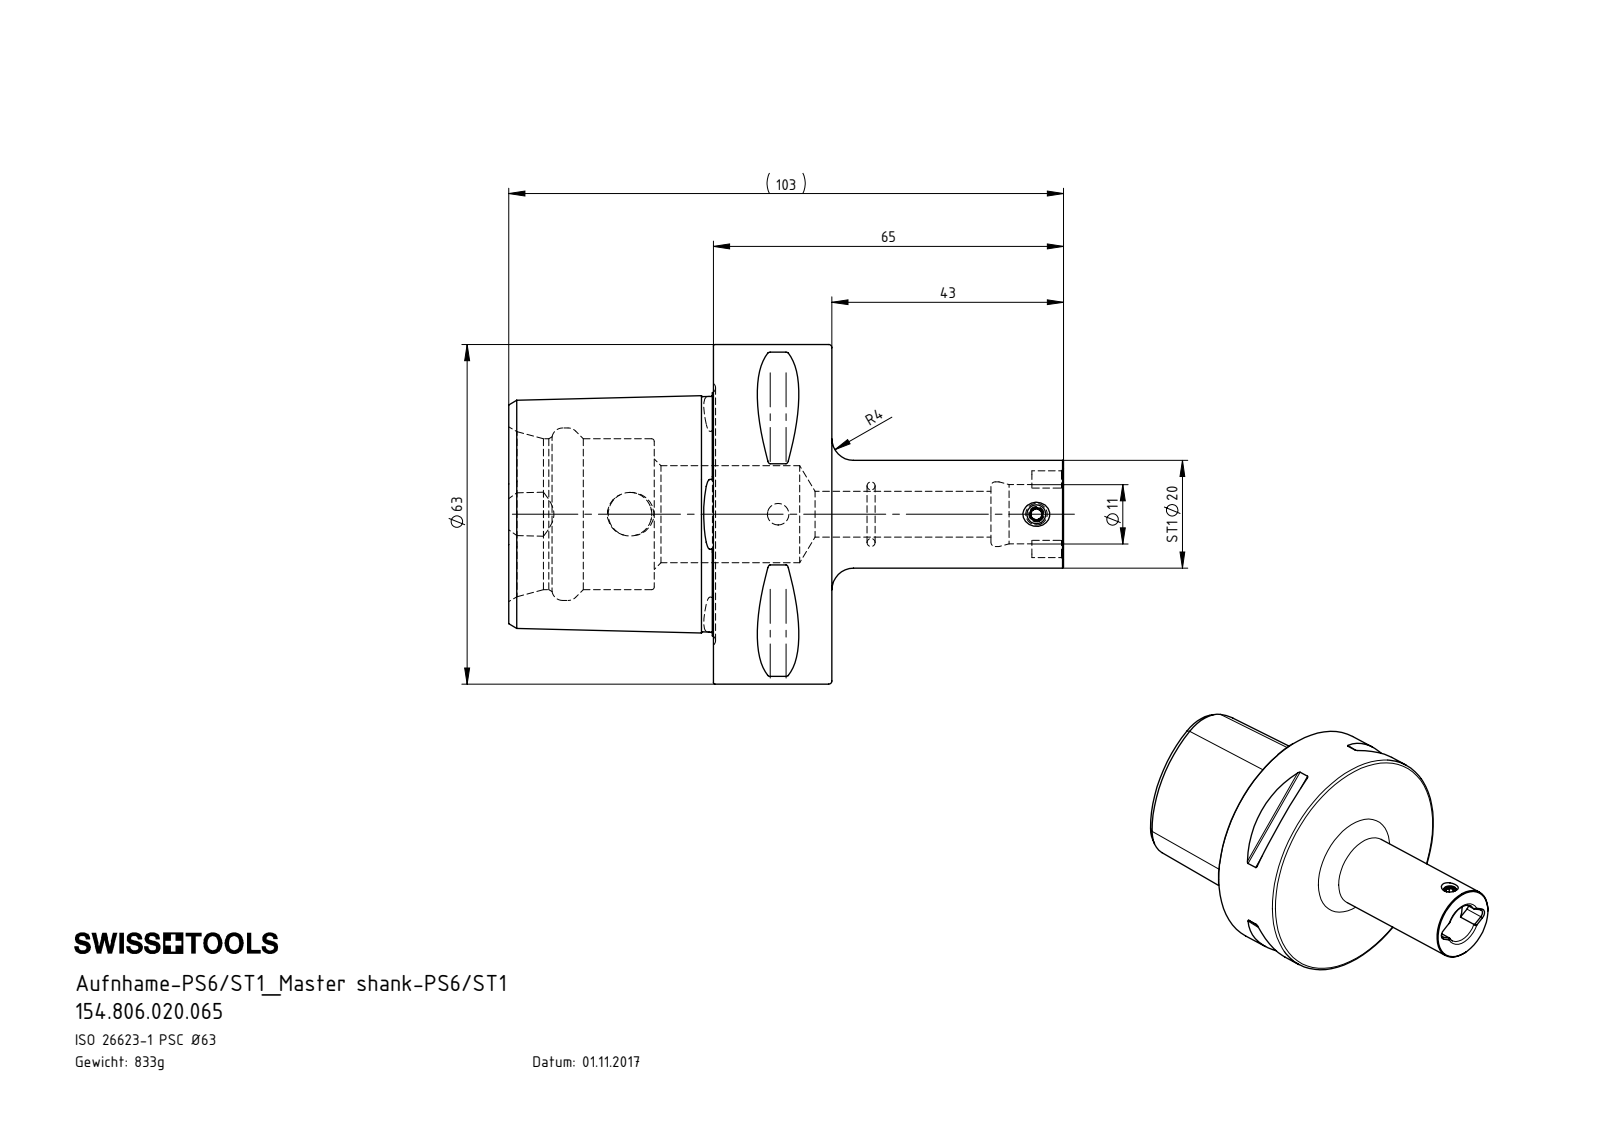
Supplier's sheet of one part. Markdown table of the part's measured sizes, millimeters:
| quantity | value |
| --- | --- |
| part name | DIN 3771 - 9x1.5; ST1-ER1.001.005_A; PS6-ST1.K01.065_B; PS6.ST1.K01.065 |
| STEP written by | SolidWorks 2017 (AUTOMOTIVE_DESIGN) |
| units | millimeters |
| bodies | 3 solids, 133 faces (43 planar, 26 cylindrical, 64 other) |
| overall size | 103 × 63 × 63 |
| volume | 106 156 mm³ |
| surface area | 24 101 mm² |
| round holes (diameter × count) | 2 × 1, 3.5 × 1, 4 × 1, 8.1 × 1, 8.5 × 1, 11 × 1, 12 × 1, 18 × 1, 28 × 1, 32 × 1 |
| round bosses / shafts (diameter × count) | 63 × 1, 20 × 1, 4 × 1 |
| partial cylindrical surfaces (radius × count) | 0.5 × 8, 1.3 × 2, 6 × 1 |
| main face-to-face distances | 22, 38, 60, 24.88, 27, 11, 33, 55.8, 103, 76 |
| hole center spacings | 27.5, 47.95, 75.45 |
